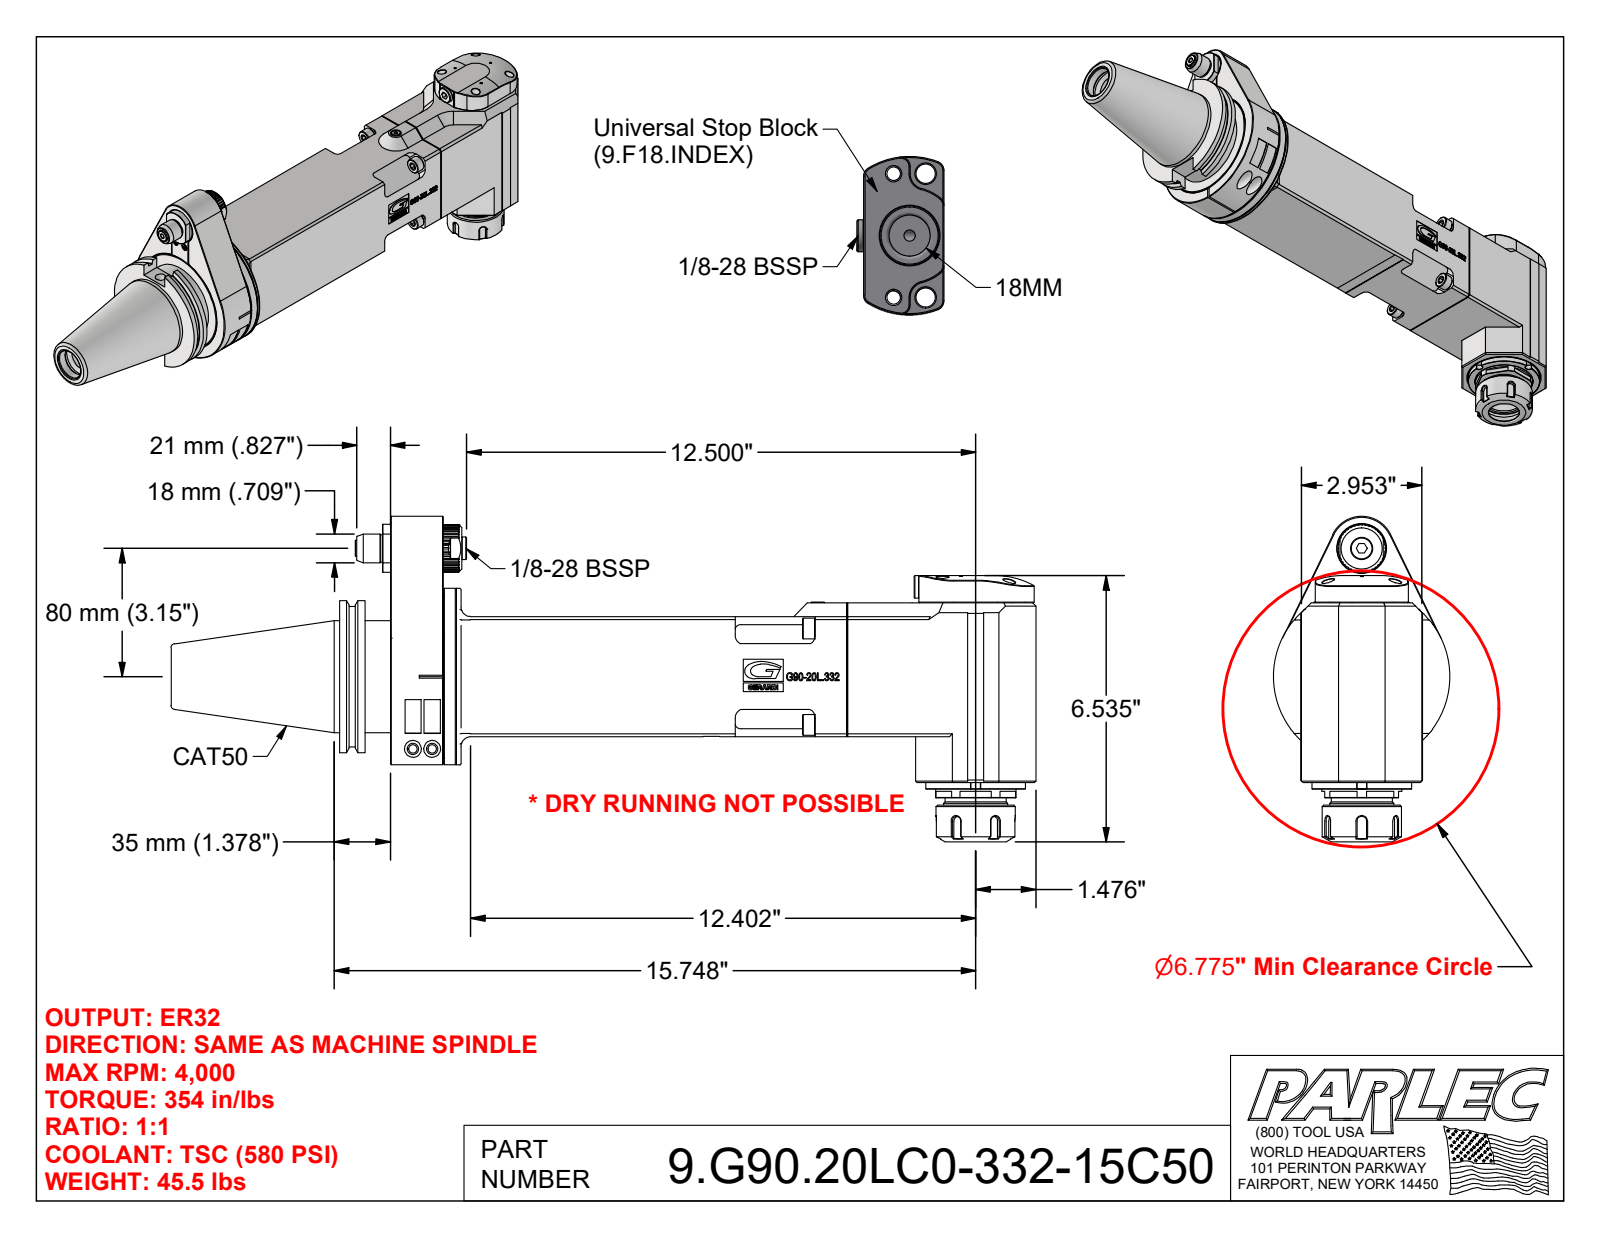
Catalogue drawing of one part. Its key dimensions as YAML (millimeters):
part_name: "9.G90.20LC0-332-15C50; 9_GA2_458_1 (Classic, Type 2, Cat50, 80mm); G90-20LC-332"
step_written_by: "Autodesk Inventor 2022 (AUTOMOTIVE_DESIGN)"
units: millimeters
bodies: {solids: 22, faces: 1622, planar: 750, cylindrical: 298, other: 574}
overall_size: [539.3, 203, 110]
volume: 1850000
surface_area: 392100
round_holes:
  - {diameter: 5, count: 12}
  - {diameter: 3.3, count: 5}
  - {diameter: 2.5, count: 4}
  - {diameter: 4.5, count: 4}
  - {diameter: 7.5, count: 4}
  - {diameter: 8.5, count: 4}
  - {diameter: 1.5, count: 3}
  - {diameter: 4, count: 3}
  - {diameter: 6, count: 3}
  - {diameter: 7, count: 2}
  - {diameter: 9.2, count: 2}
  - {diameter: 10.5, count: 2}
round_bosses_or_shafts:
  - {diameter: 13, count: 5}
  - {diameter: 14, count: 2}
  - {diameter: 10, count: 2}
  - {diameter: 9, count: 2}
  - {diameter: 110, count: 1}
  - {diameter: 102, count: 1}
  - {diameter: 98.4, count: 1}
  - {diameter: 91.3, count: 1}
partial_cylinders:
  - {radius: 3, count: 9}
  - {radius: 4, count: 8}
  - {radius: 2.5, count: 5}
  - {radius: 20, count: 5}
  - {radius: 6, count: 4}
  - {radius: 2.2, count: 2}
  - {radius: 5, count: 2}
  - {radius: 5.7, count: 2}
face_to_face_distances: [75, 33, 15.9, 5, 8, 4.5, 0.5, 3, 48.9, 369.5]
hole_center_spacings: [47.5, 33.1, 82.3, 14.5, 15, 24.6, 29.5, 41.7]
